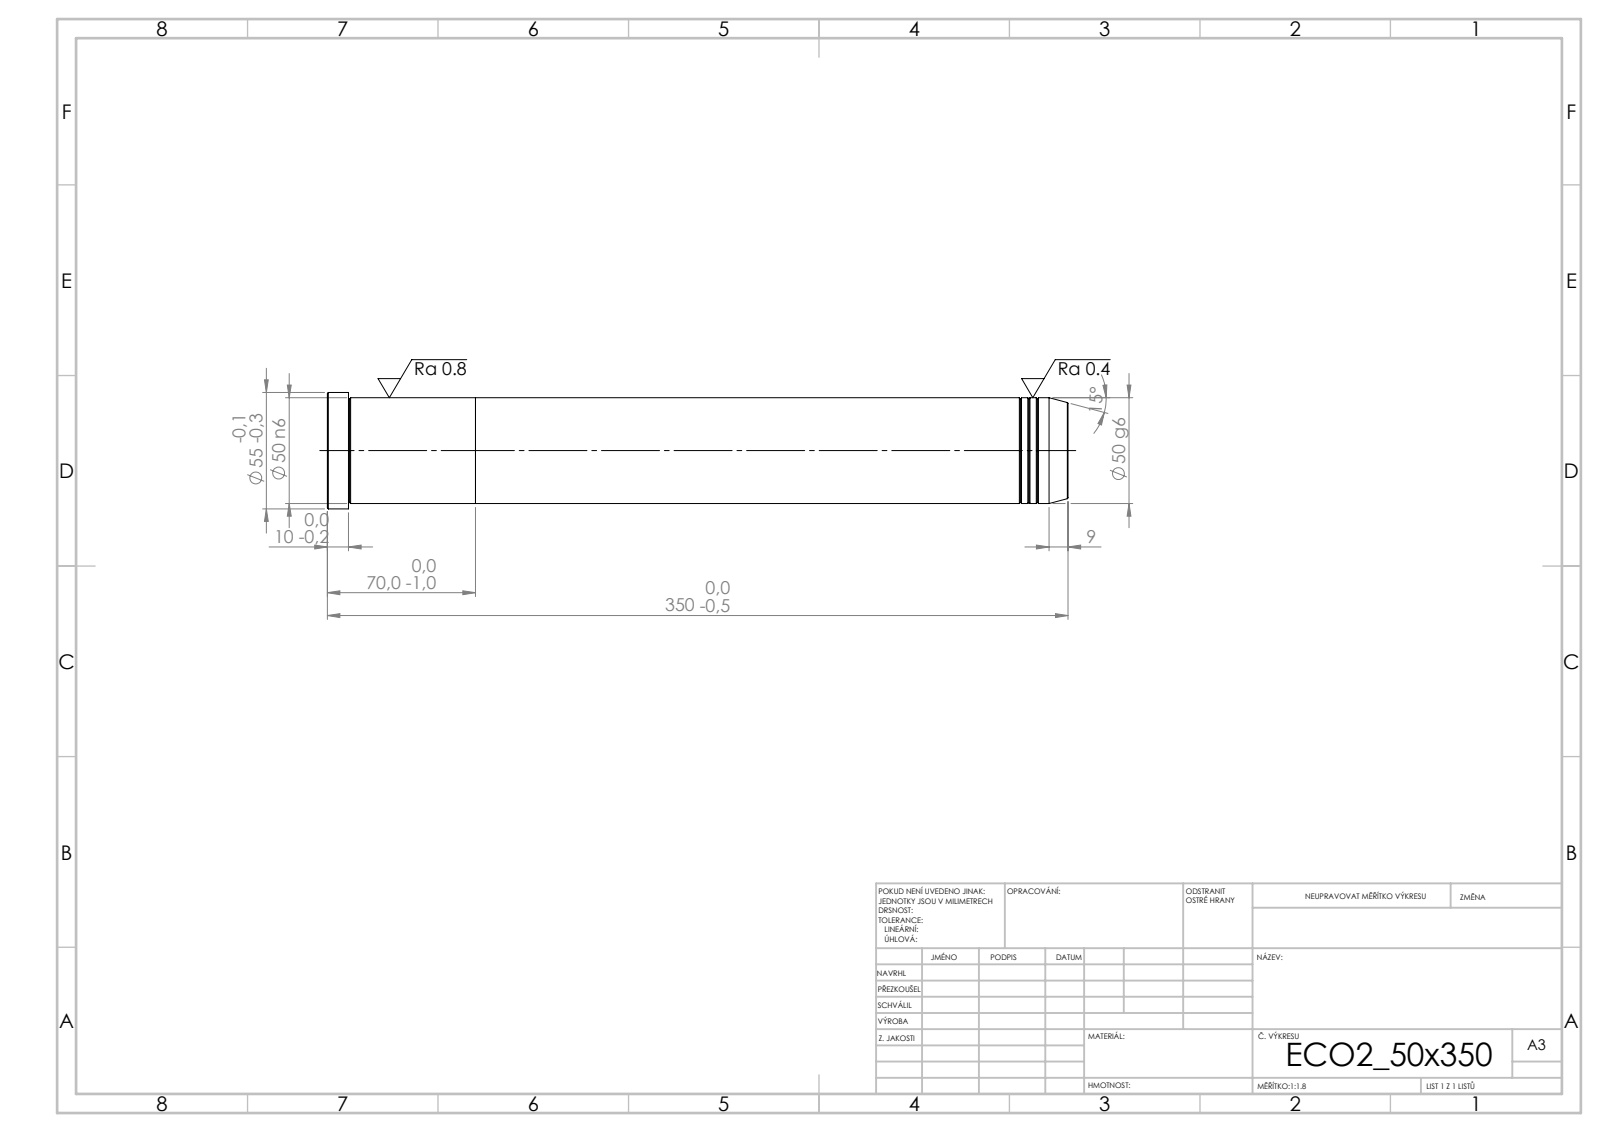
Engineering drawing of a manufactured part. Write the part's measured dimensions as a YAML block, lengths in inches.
step_written_by: "SolidWorks 2019 (CONFIG_CONTROL_DESIGN)"
units: inches
bodies: {solids: 2, faces: 39, planar: 5, cylindrical: 12, other: 22}
overall_size: [13.78, 2.165, 2.165]
volume: 42.07
surface_area: 98.75
round_bosses_or_shafts:
  - {diameter: 2.165, count: 1}
  - {diameter: 1.969, count: 1}
face_to_face_distances: [2.756, 11.024, 13.78, 13.386, 2.362, 0.394]
